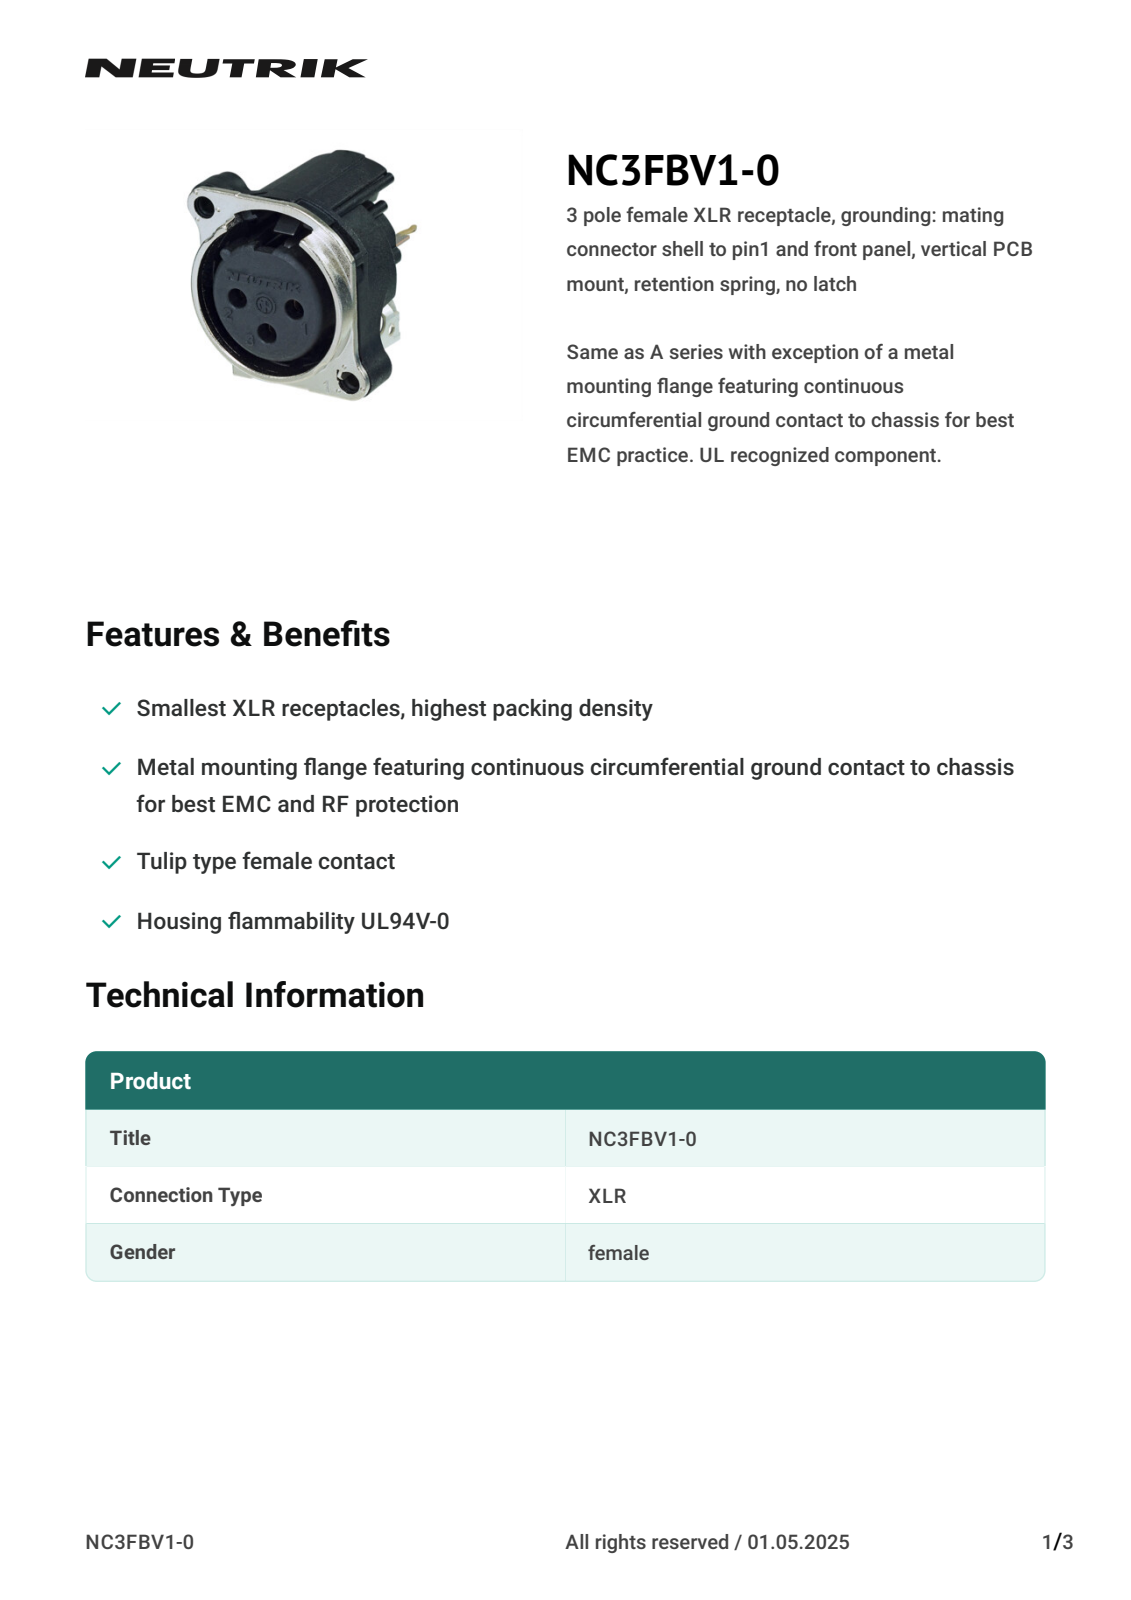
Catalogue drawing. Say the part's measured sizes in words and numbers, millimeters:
The part is named "NC3FBV2". Its 3-D file was written by "CREO PARAMETRIC BY PTC INC, 2019080 (CONFIG_CONTROL_DESIGN)". It is 1 solid with 1665 faces: 689 planar, 422 cylindrical and 554 other. Overall it measures 31.11 by 26.8 by 25.3 millimeters. Its volume is 5 965 cubic millimeters and its surface area 5 272 square millimeters. Round holes: 4 of diameter 2.5, 2 of diameter 1.27, 2 of diameter 1.5, 2 of diameter 2.1, 2 of diameter 3.5, 1 of diameter 2.8, 1 of diameter 19.5, 1 of diameter 20.5. Round bosses or shafts: 2 of diameter 1.5, 1 of diameter 15.8, 1 of diameter 3. Partial cylindrical surfaces (rounded edges, fillets, slot ends): 211 of radius 0.2, 21 of radius 0.15, 13 of radius 1, 9 of radius 0.1, 9 of radius 0.12, 9 of radius 0.5, 8 of radius 0.4, 6 of radius 0.75. The main face-to-face distances are 0.5, 0.75, 2.95, 3.7, 13, 16.51, 17.26, 20.21, 9.3, 5.71. The hole center spacings are 3.22, 4.05, 5.66, 8.64, 11.5, 11.62, 14, 15.12.
